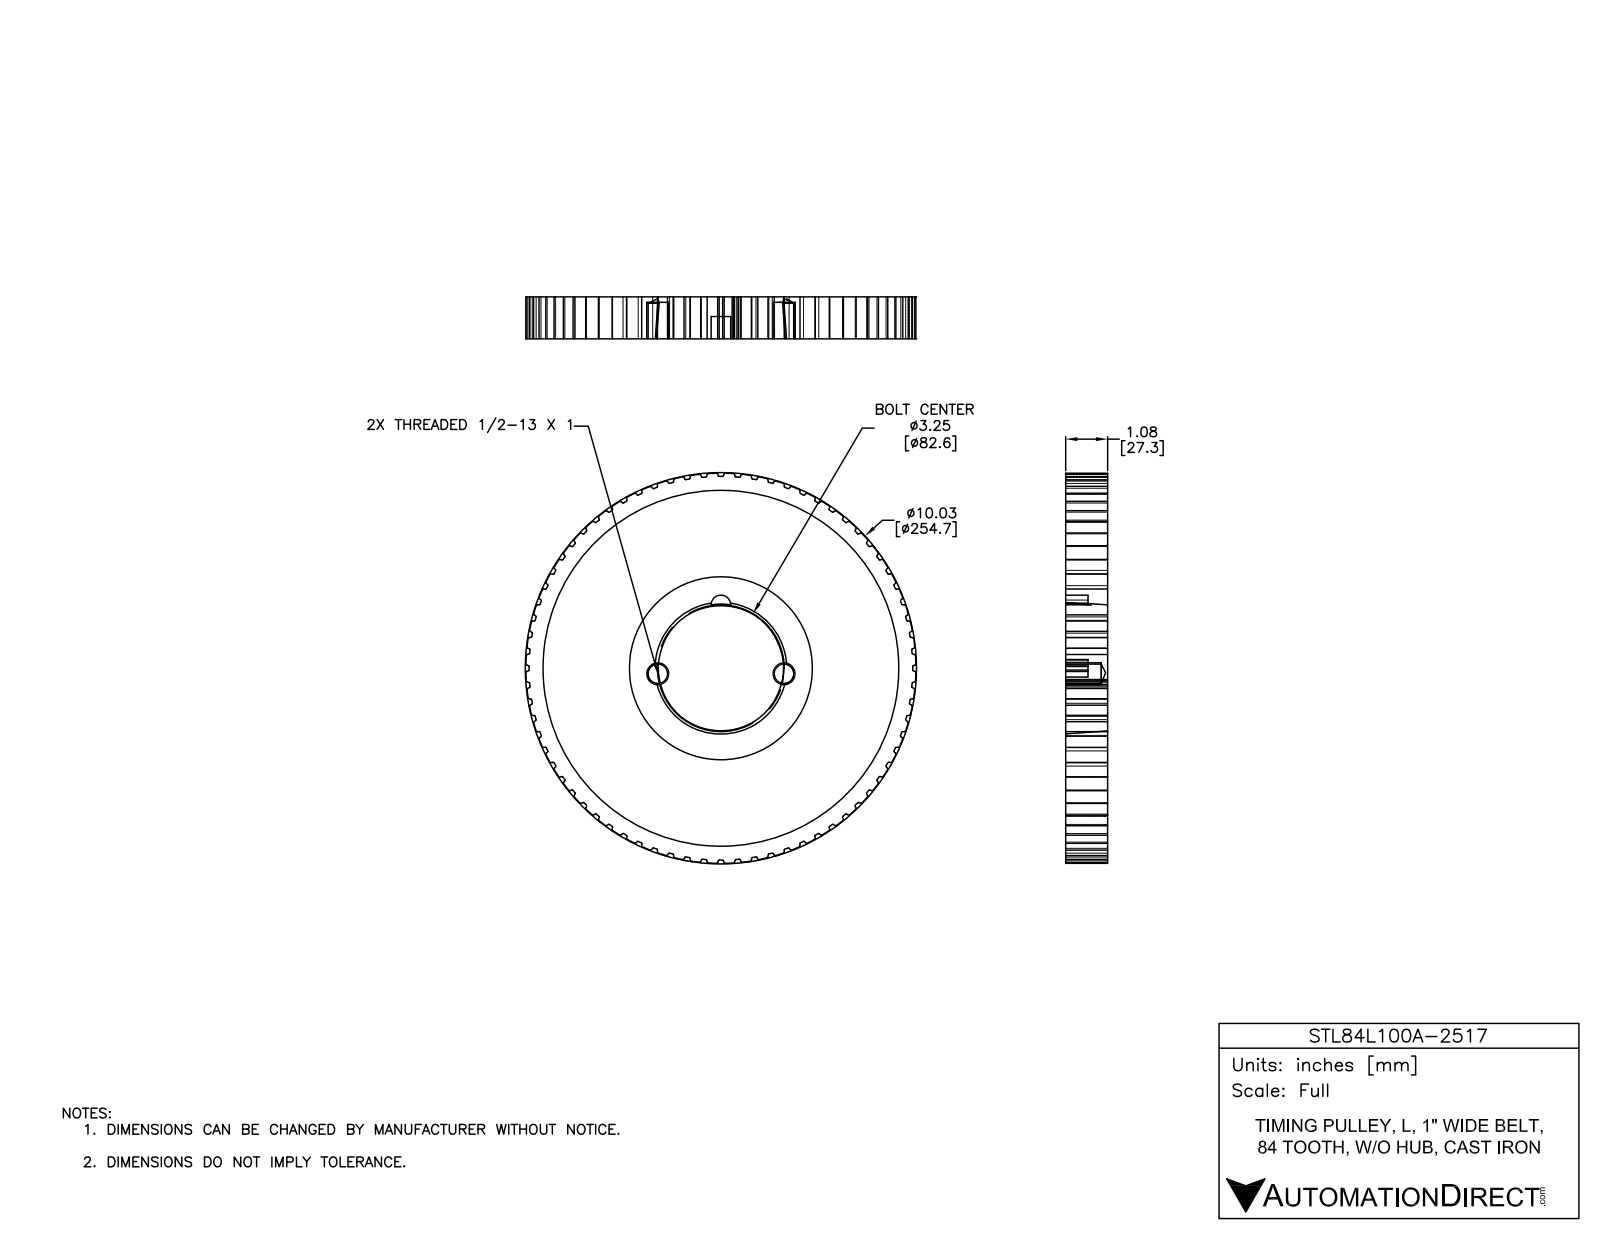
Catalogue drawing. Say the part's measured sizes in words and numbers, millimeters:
The part is named "STL84L100A-2517". Its 3-D file was written by "SolidWorks 2015 (AUTOMOTIVE_DESIGN)". It is 1 solid with 762 faces: 259 planar, 501 cylindrical and 2 other. Overall it measures 254 by 254 by 27.33 millimeters. Its volume is 715 328 cubic millimeters and its surface area 141 907 square millimeters. Round holes: 1 of diameter 231.6. Round bosses or shafts: 1 of diameter 118.88, 1 of diameter 118.88. Partial cylindrical surfaces (rounded edges, fillets, slot ends): 168 of radius 0.38, 168 of radius 0.51, 2 of radius 4.7, 1 of radius 5.71, 1 of radius 127. The main face-to-face distances are 11.29, 8, 19.29, 27.29, 8.04, 19.33, 27.33, 82.58, 82.55, 82.61.
